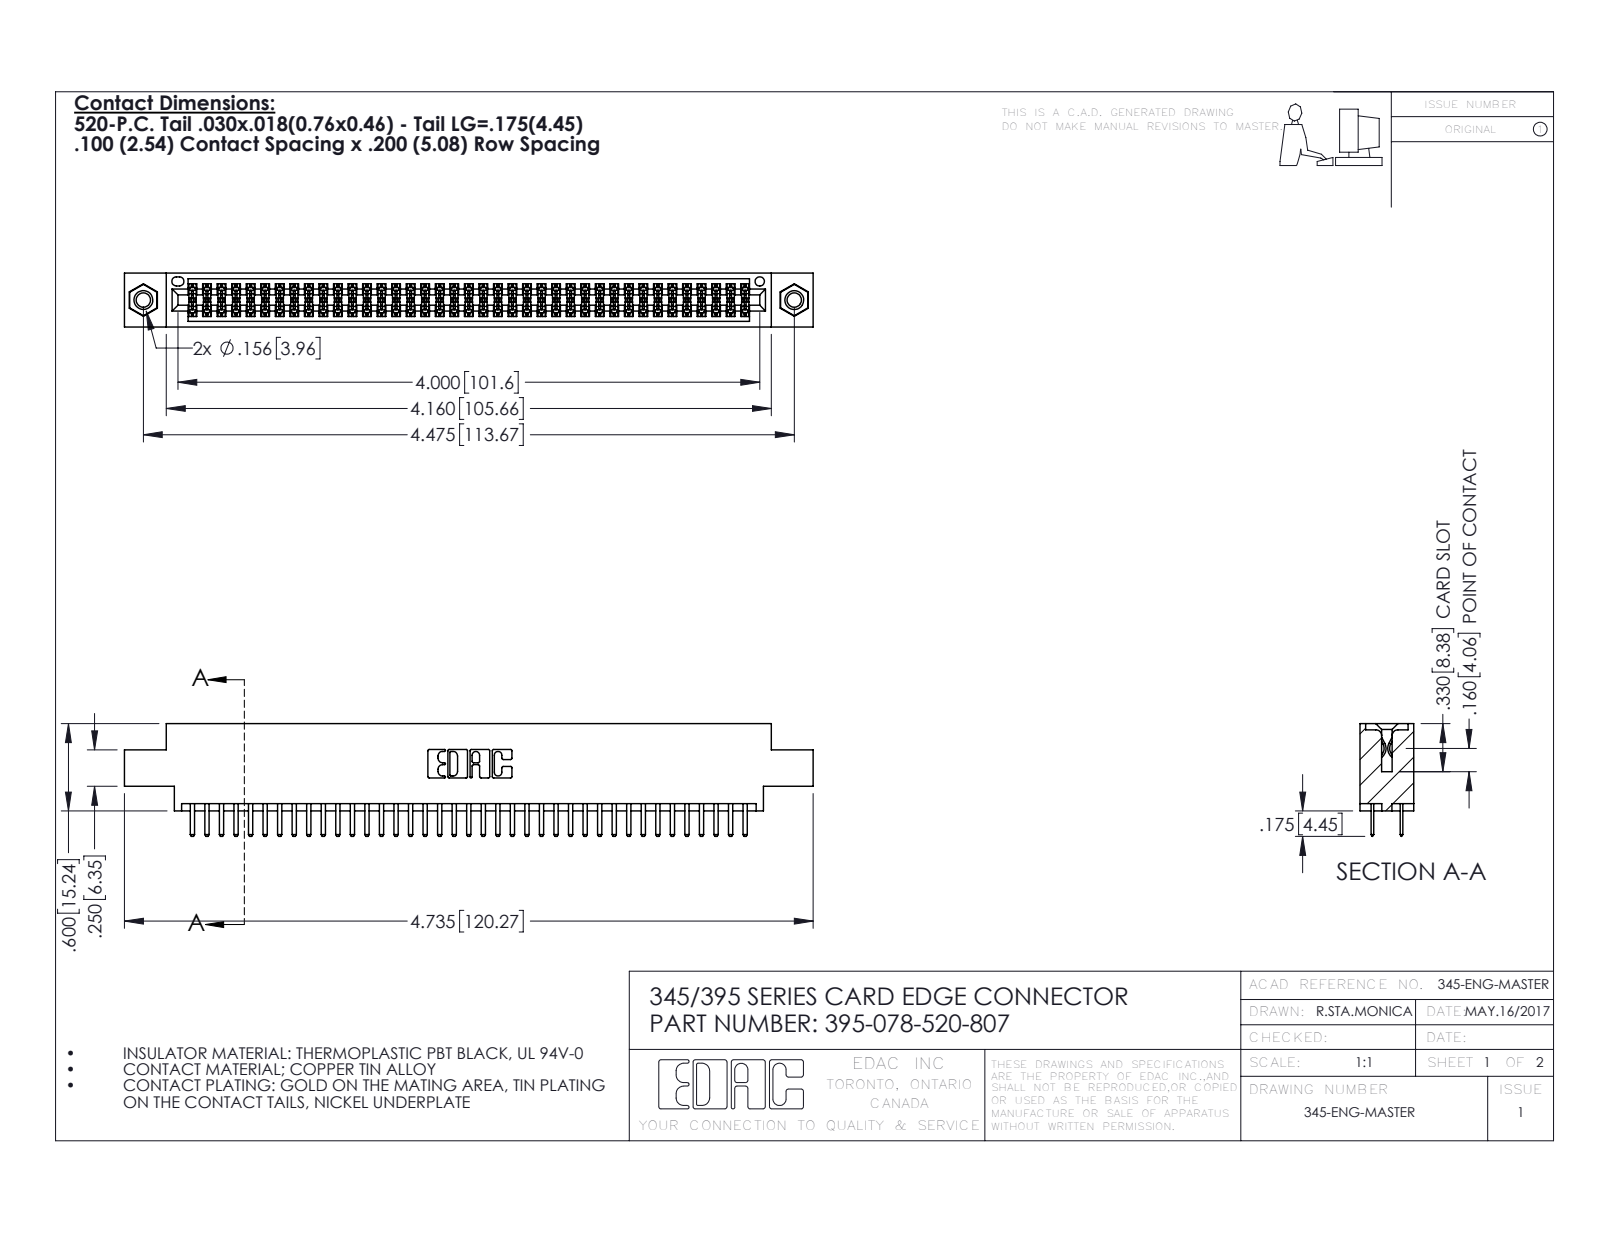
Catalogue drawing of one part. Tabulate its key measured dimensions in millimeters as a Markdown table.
| quantity | value |
| --- | --- |
| part name | 395-078-520-807; 345-292-001_345-293-120; 345-250-001_345-250-005-103; 345 Part_0.170 Offset - 0.156 Dia-TI |
| STEP written by | SolidWorks 2016 (CONFIG_CONTROL_DESIGN) |
| units | millimeters |
| bodies | 81 solids, 4402 faces (2846 planar, 1540 cylindrical, 16 other) |
| overall size | 120.3 × 19.7 × 9.4 |
| volume | 11 500 mm³ |
| surface area | 17 030 mm² |
| round holes (diameter × count) | 2.5 × 2, 3.2 × 2, 4 × 2, 1.6 × 1 |
| round bosses / shafts (diameter × count) | 3.9 × 2 |
| partial cylindrical surfaces (radius × count) | 0.2 × 117, 0.3 × 82, 0.3 × 22, 0.2 × 6, 0.8 × 6, 0.7 × 3, 0.4 × 2, 0.5 × 2 |
| main face-to-face distances | 1.8, 7.6, 5.1, 9.4, 2.5, 6.9, 0.6, 5.7, 0.6, 4.4 |
| hole center spacings | 6.9, 107.7, 113.7 |
